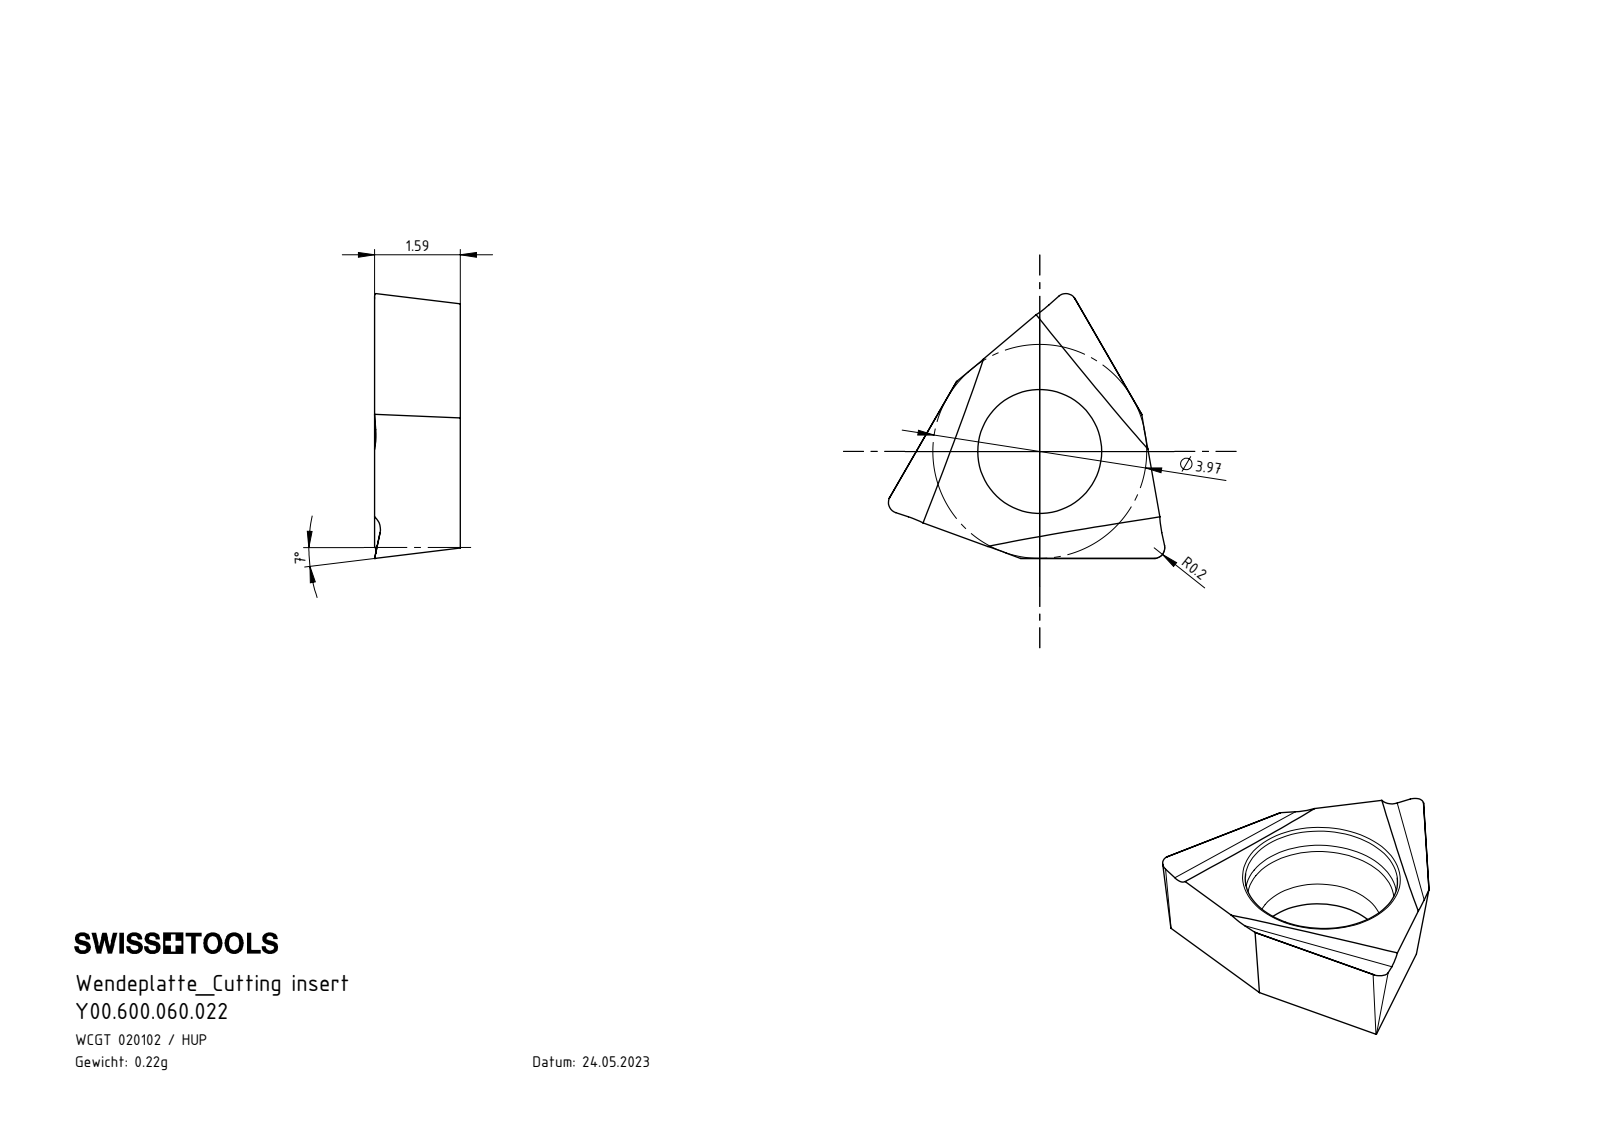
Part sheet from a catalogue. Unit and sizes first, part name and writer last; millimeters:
Units: millimetres
Overall size (bounding box): 5.13 × 4.92 × 1.59
Round holes (diameter × count): ⌀2.3 ×1
Partial cylindrical surfaces — rounded edges, fillets, slot ends (radius × count): R0.3 ×3
Main face-to-face distances: 1.59
Volume: 15 mm³ · Surface area: 56 mm²
Bodies: 1 solid, 31 faces (14 planar, 5 cylindrical, 12 other)
Part name (STEP PRODUCT): Y00.600.060.022
STEP written by: SolidWorks 2022 (AUTOMOTIVE_DESIGN)
